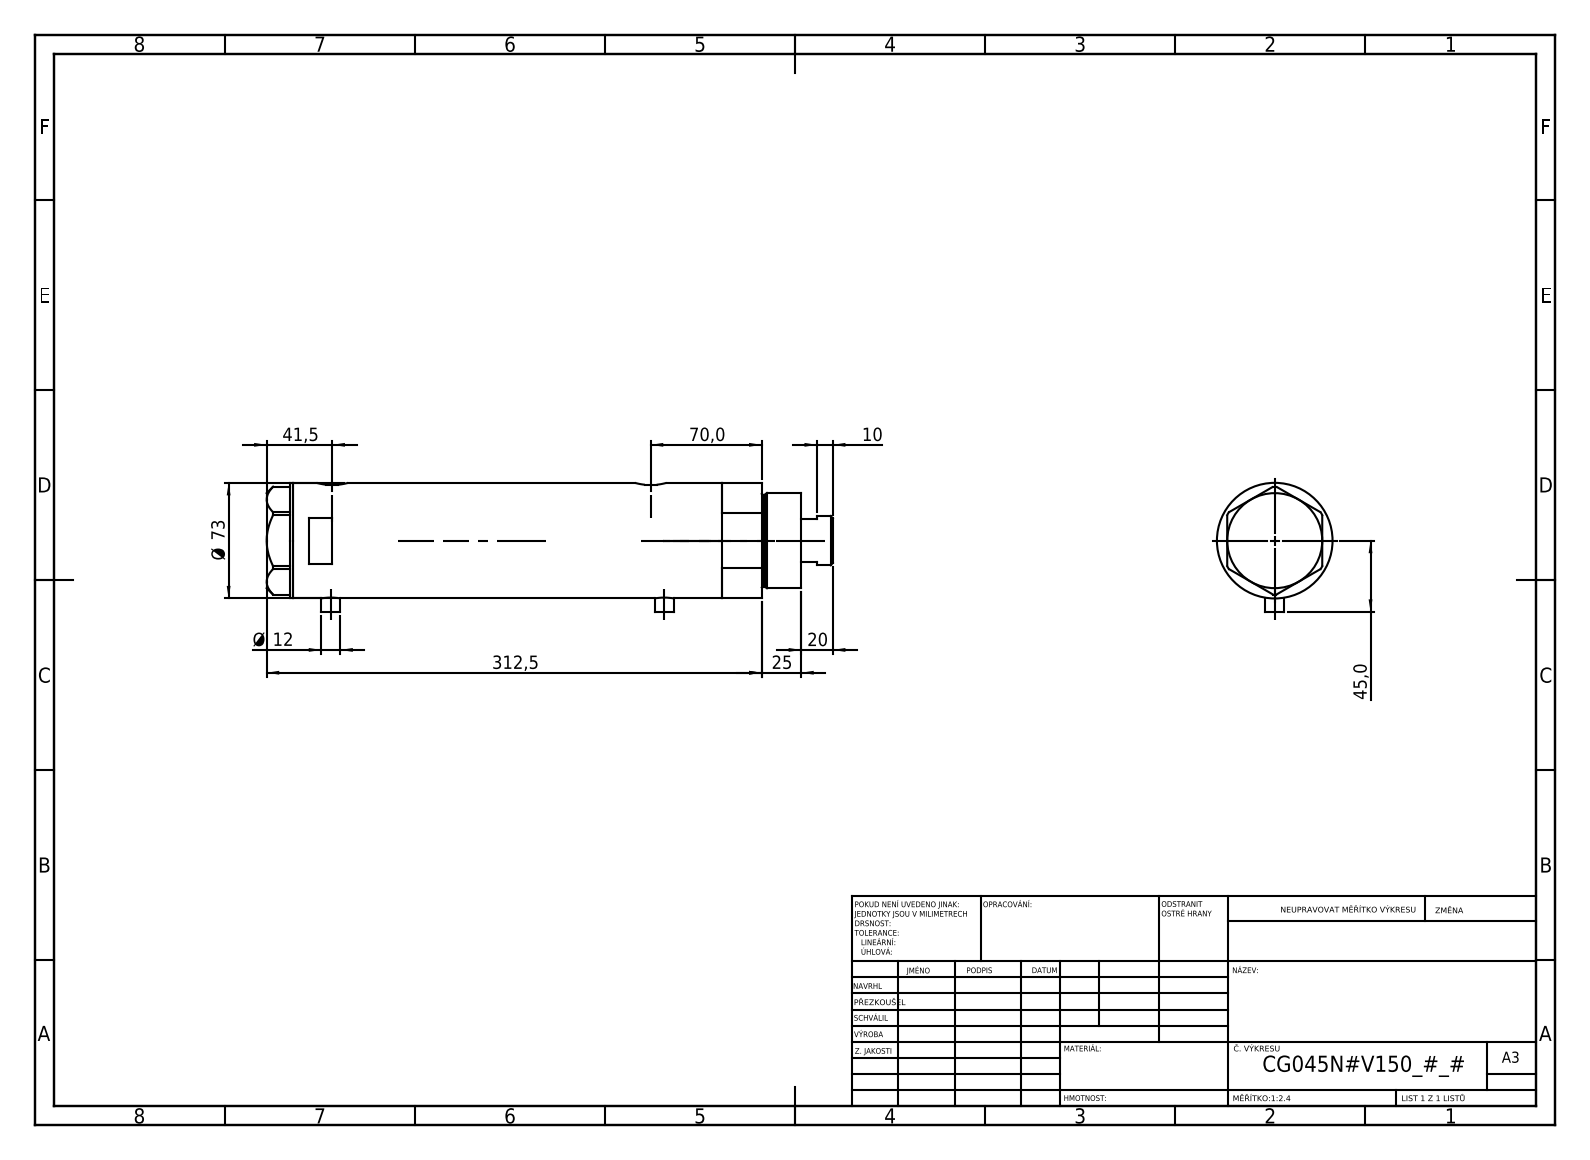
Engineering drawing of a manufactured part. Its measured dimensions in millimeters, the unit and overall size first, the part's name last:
Units: millimetres
Overall size (bounding box): 357.5 × 81.5 × 73
Round holes (diameter × count): ⌀12.5 ×2, ⌀13.16 ×2, ⌀10.5 ×1, ⌀32 ×1, ⌀33.5 ×1, ⌀45 ×1, ⌀48 ×1, ⌀64 ×1
Round bosses / shafts (diameter × count): ⌀12 ×2, ⌀73 ×1, ⌀60 ×1, ⌀58 ×1, ⌀31 ×1
Partial cylindrical surfaces — rounded edges, fillets, slot ends (radius × count): R10 ×2
Main face-to-face distances: 226, 26, 200, 16.5, 42.5, 242.5, 2, 321, 337.5, 295
Hole centre spacings: 1, 8.5, 201, 202, 209.5, 210.5
Volume: 1 247 000 mm³ · Surface area: 198 635 mm²
Bodies: 4 solids, 120 faces (49 planar, 51 cylindrical, 20 other)
Part name (STEP PRODUCT): V270CG_FRONT; V270CG_VC; V270CG_BACK; V270CG_MIDDLE
STEP written by: SolidWorks 2019 (CONFIG_CONTROL_DESIGN)
